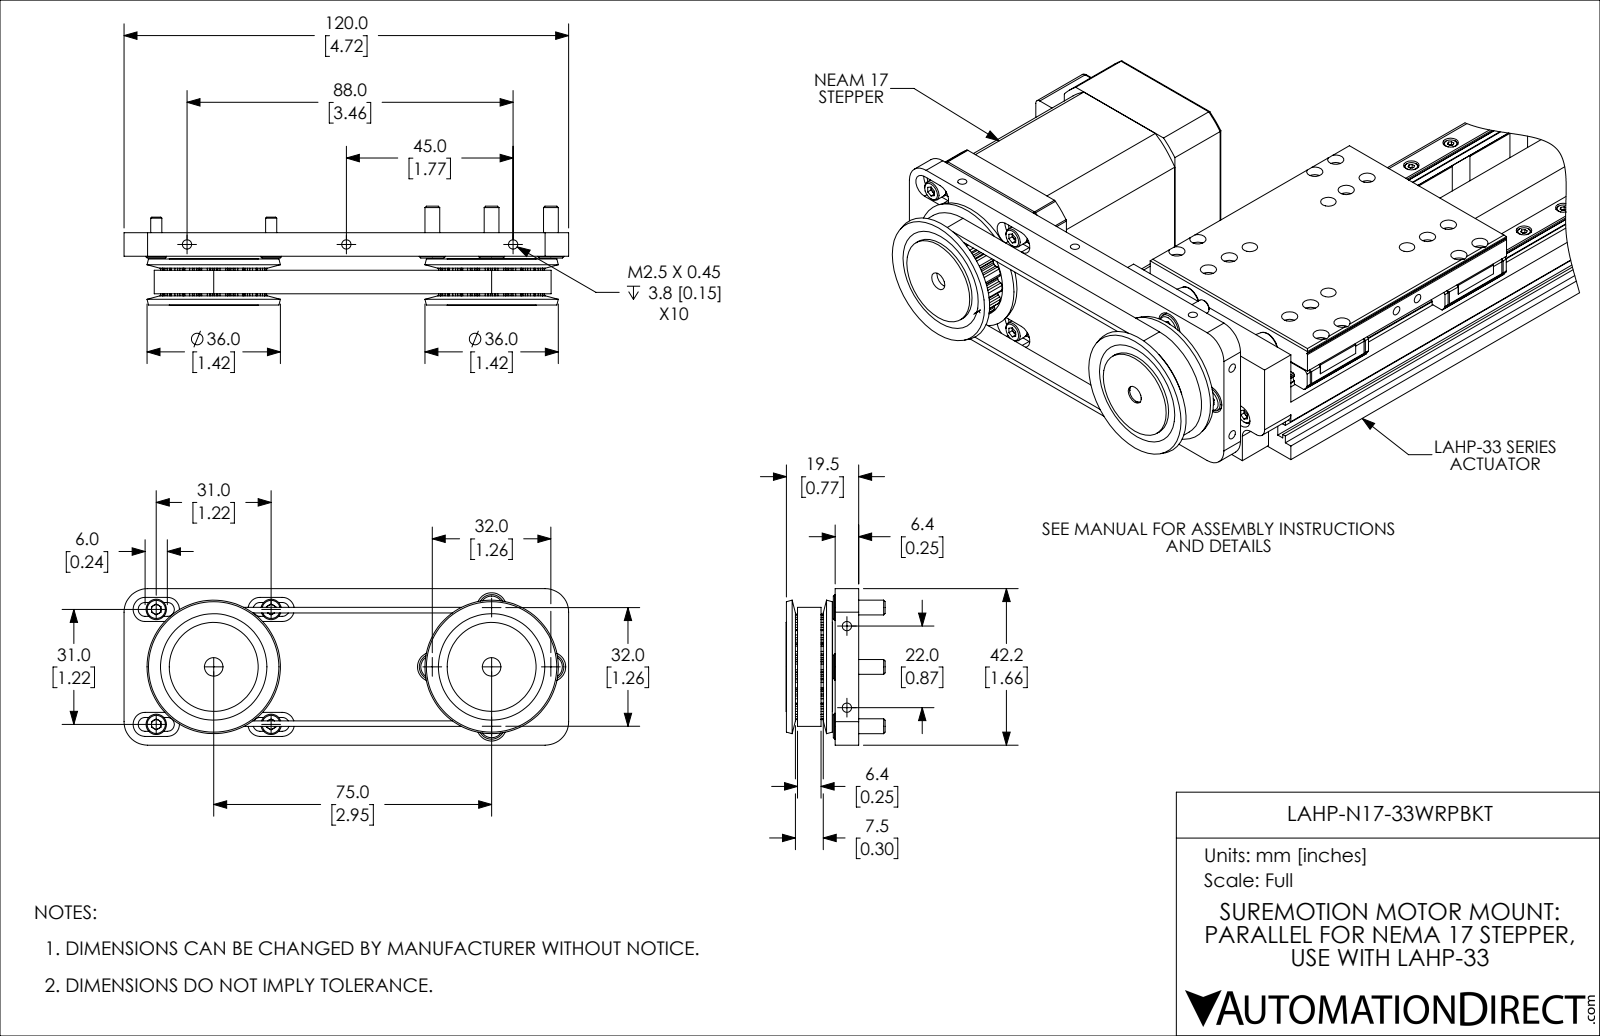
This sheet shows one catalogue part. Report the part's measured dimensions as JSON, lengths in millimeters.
{"part_name": "LAHP-N17-33WRPBKT", "step_written_by": "SolidWorks 2019 (CONFIG_CONTROL_DESIGN)", "units": "millimeters", "bodies": {"solids": 20, "faces": 799, "planar": 298, "cylindrical": 393, "other": 108}, "overall_size": [120, 42.2, 26.7], "volume_mm3": 43510, "surface_area_mm2": 27860, "round_holes": [[2.5, 5], [3.2, 4], [3.3, 4], [4.3, 4], [4.5, 4], [8, 4], [5, 2], [22, 1]], "round_bosses_or_shafts": [[7, 4], [5.5, 4], [4, 4], [3, 4], [24, 2]], "partial_cylinders_radius": [[0.6, 144], [1.9, 8], [3.3, 8], [6.4, 4], [11, 2], [12.9, 2], [14.3, 2], [14.6, 2]], "face_to_face_distances": [6.4, 1.5, 30.6, 19.6, 13.2, 7.1, 0.7, 12.5, 0.9, 11.6], "hole_center_spacings": [16, 21.9, 22.6, 31, 32, 43.8, 46.2, 59.5]}
